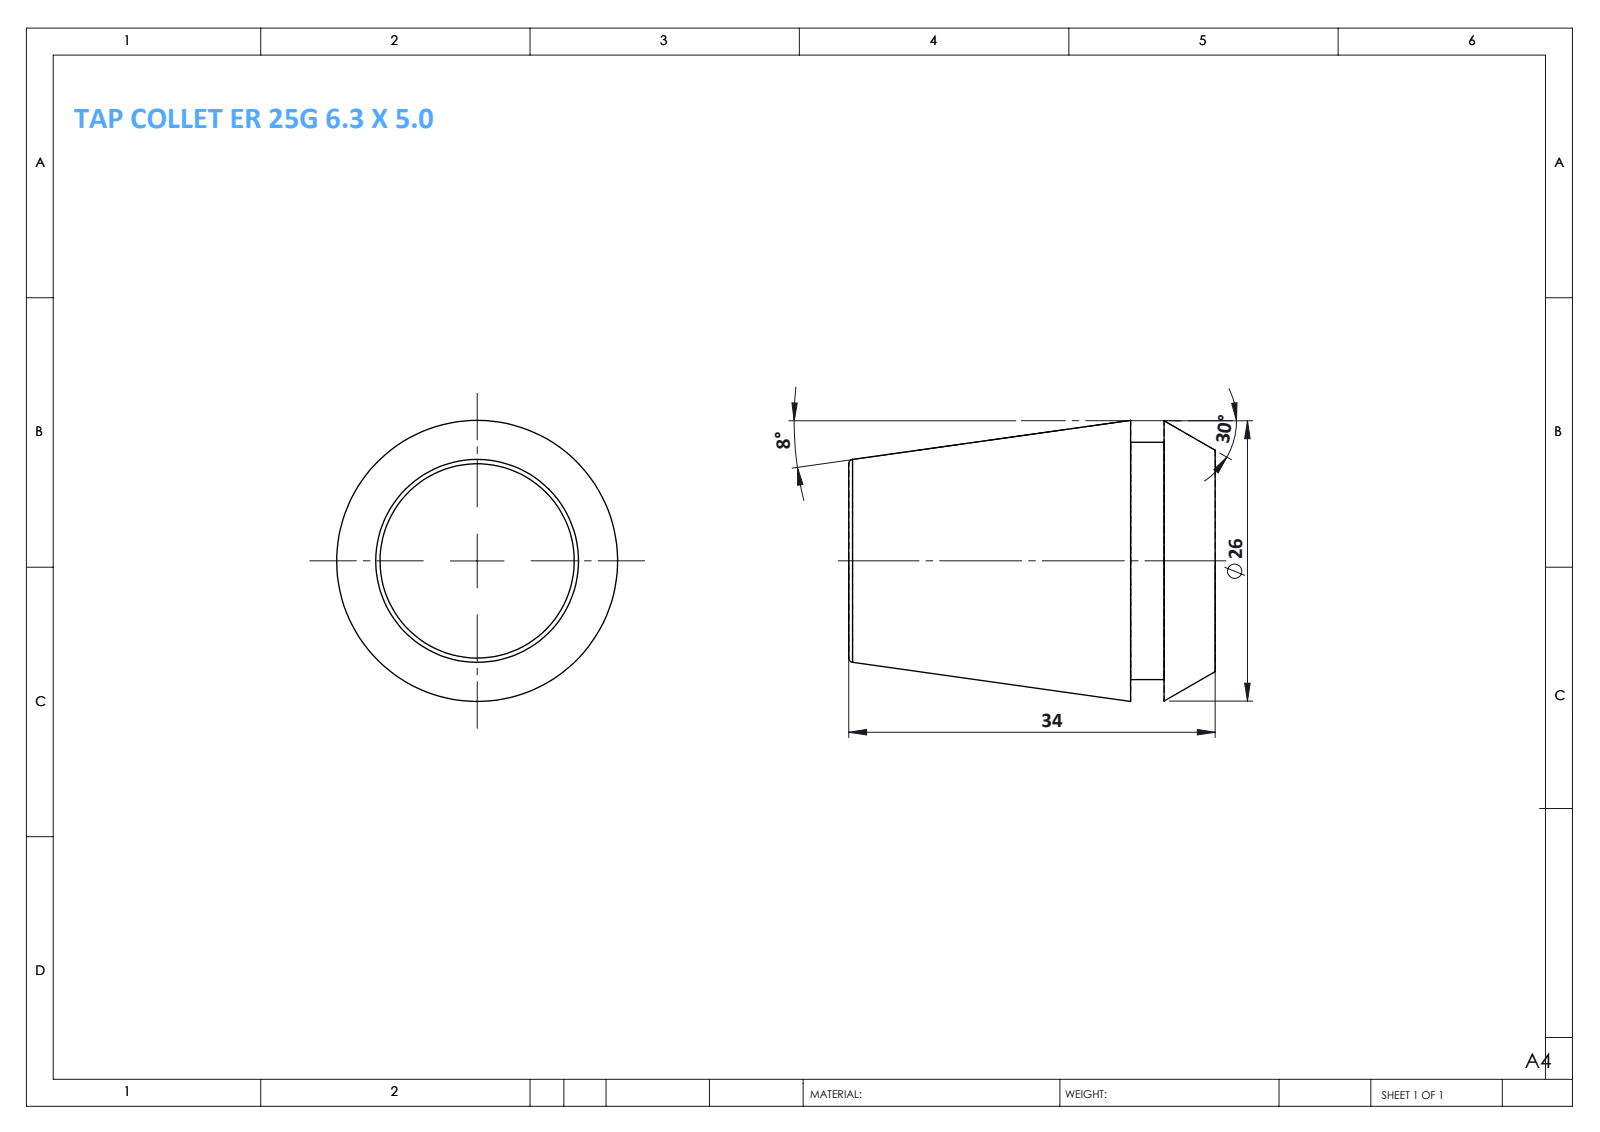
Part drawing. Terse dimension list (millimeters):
name: TAP COLLET ER 25G 6.3 X 5.0
written by: SolidWorks 2014 (CONFIG_CONTROL_DESIGN)
unit: mm
bodies: 1 solid, 12 faces (4 planar, 2 cylindrical, 6 other)
size: 34 × 26.07 × 26.07
volume: 13 600 mm³; area: 3 376 mm²
bosses: 1× ⌀22
face distances: 34, 7.84, 26.16, 4.74, 3.1, 29.26
